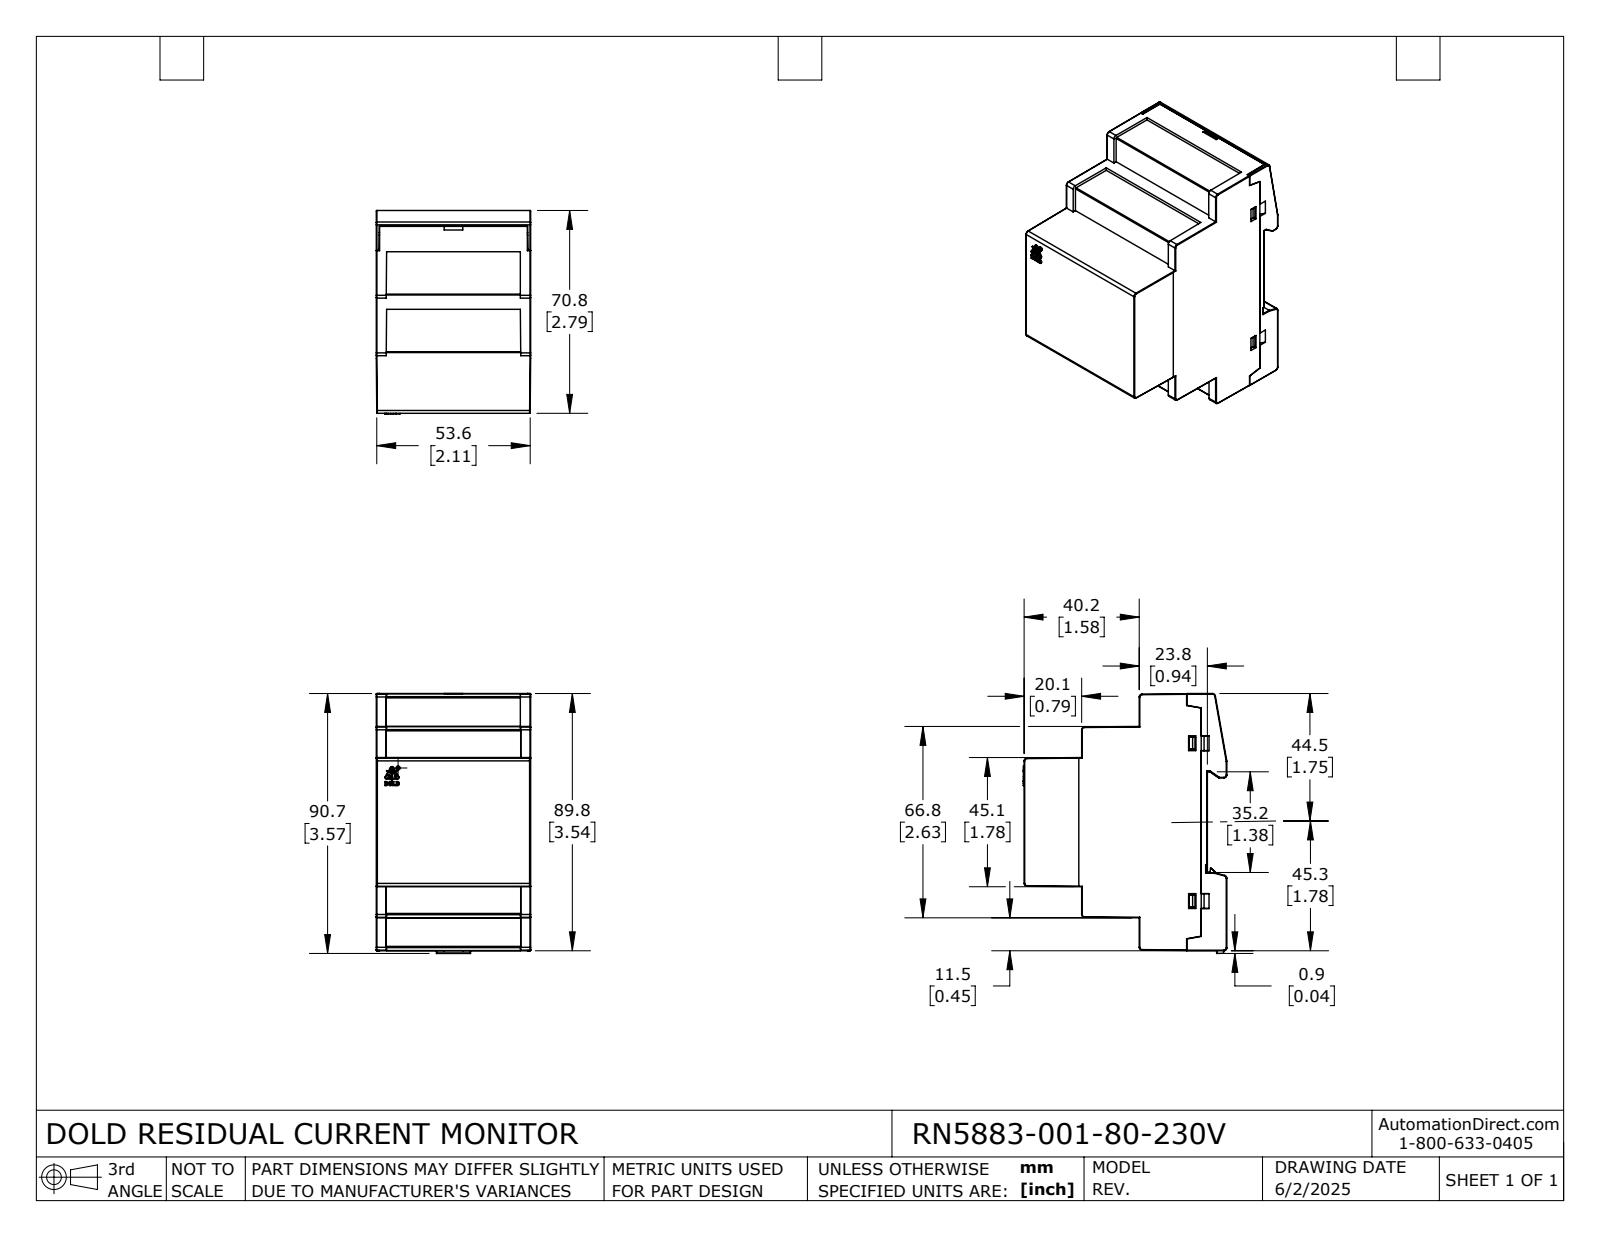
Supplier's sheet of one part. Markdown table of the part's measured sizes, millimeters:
| quantity | value |
| --- | --- |
| part name | RN5883-001-80-230V |
| STEP written by | SolidWorks 2024 (AUTOMOTIVE_DESIGN) |
| units | millimeters |
| bodies | 13 solids, 1307 faces (1035 planar, 186 cylindrical, 86 other) |
| overall size | 90.7 × 71 × 53.9 |
| volume | 232 900 mm³ |
| surface area | 52 160 mm² |
| round holes (diameter × count) | 1.2 × 1 |
| round bosses / shafts (diameter × count) | 2.5 × 6, 4 × 4, 4.6 × 1, 1.3 × 1 |
| partial cylindrical surfaces (radius × count) | 0.2 × 44, 0.1 × 19, 1 × 18, 0.5 × 11, 0.1 × 6, 0.1 × 4, 0.3 × 4, 0.5 × 3 |
| main face-to-face distances | 3.5, 53.9, 50.4, 1.6, 1.9, 52, 48.6, 1, 61.8, 2.2 |
